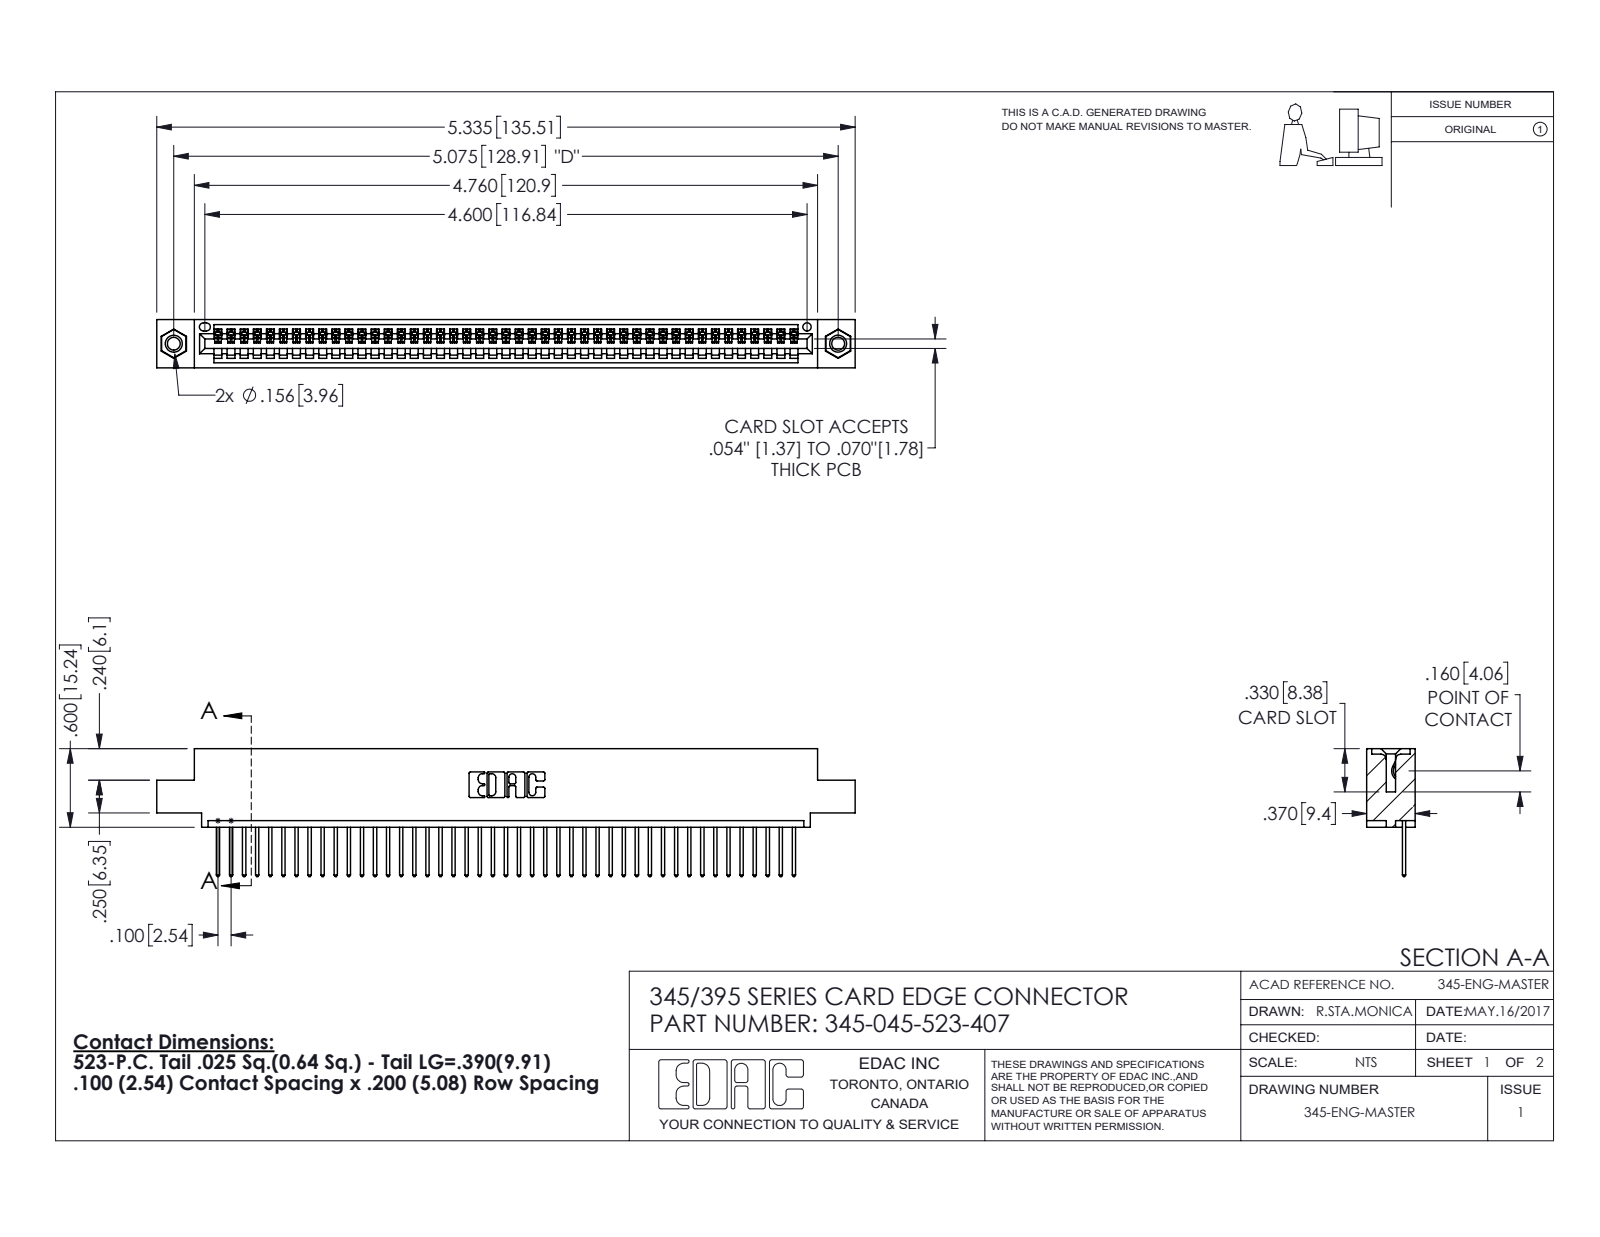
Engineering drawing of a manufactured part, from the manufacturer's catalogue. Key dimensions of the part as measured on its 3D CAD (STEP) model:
Part name (STEP PRODUCT): 345 Part_0.110 Offset - 0.156 Dia-TI; 345-250-001_345-250-005-103; 345-292-001_345-293-123; 345-045-523-407
STEP written by: SolidWorks 2016 (CONFIG_CONTROL_DESIGN)
Units: inches
Bodies: 48 solids, 2800 faces (1916 planar, 868 cylindrical, 16 other)
Overall size (bounding box): 5.335 × 0.977 × 0.37
Volume: 0.781 in³ · Surface area: 26.66 in²
Round holes (diameter × count): ⌀0.098 ×2, ⌀0.125 ×2, ⌀0.156 ×2, ⌀0.064 ×1
Round bosses / shafts (diameter × count): ⌀0.155 ×2
Partial cylindrical surfaces — rounded edges, fillets, slot ends (radius × count): R0.006 ×90, R0.01 ×90, R0.01 ×22, R0.007 ×6, R0.031 ×6, R0.026 ×3, R0.031 ×2, R0.04 ×2
Main face-to-face distances: 0.072, 0.298, 0.37, 0.2, 0.098, 0.272, 0.025, 0.225, 0.149, 0.072
Hole centre spacings: 0.27, 4.839, 5.075
